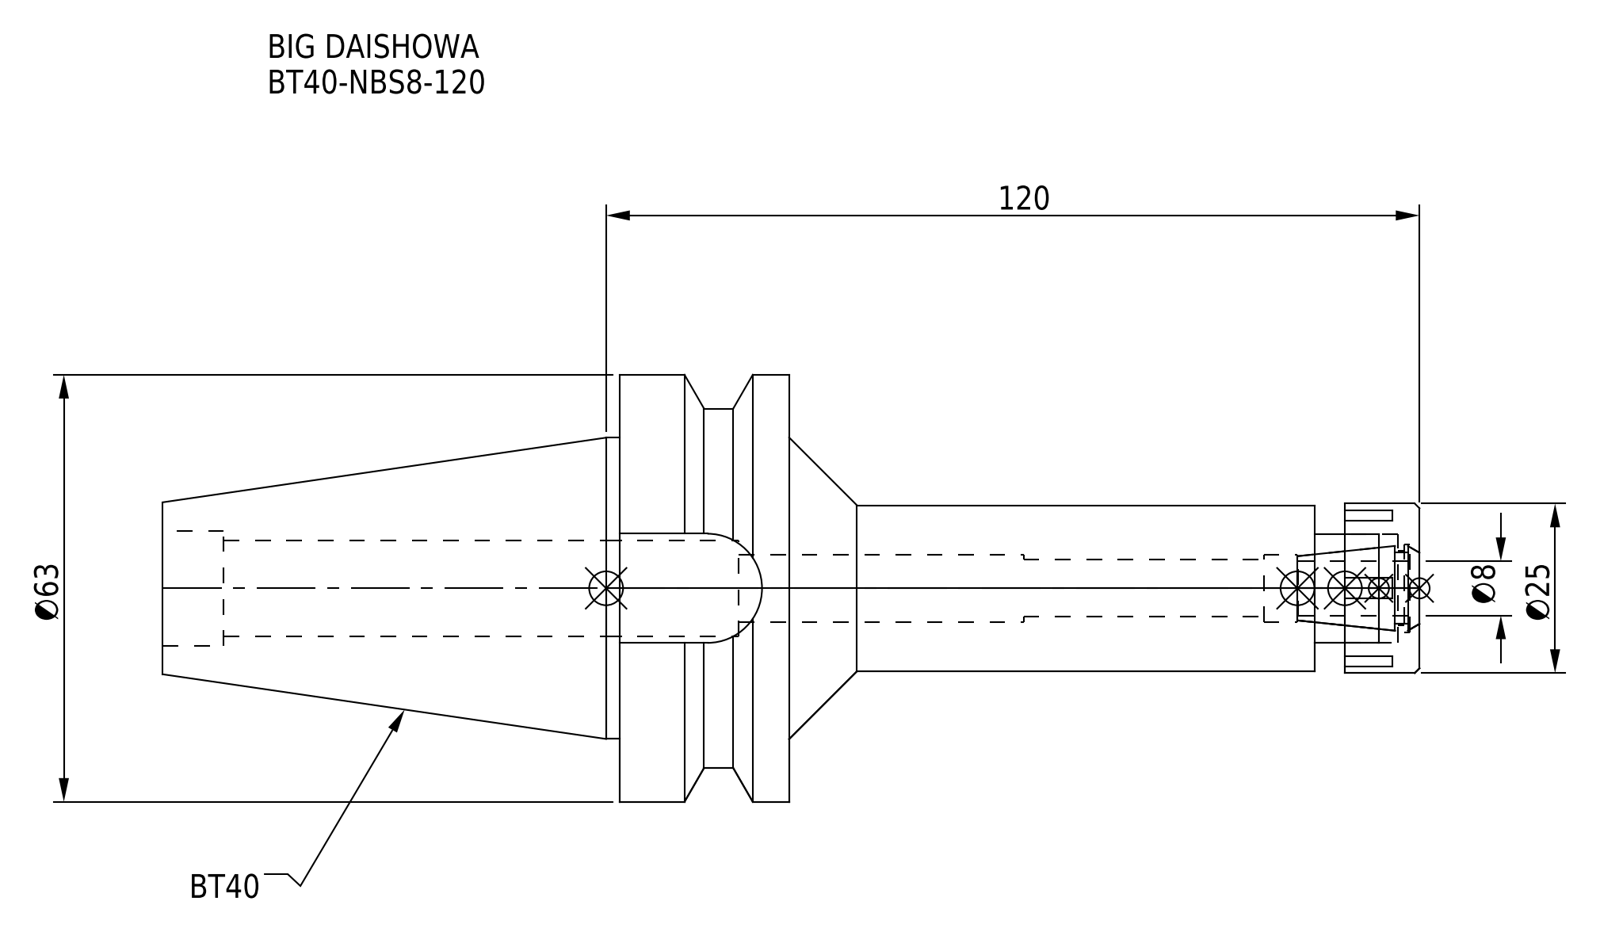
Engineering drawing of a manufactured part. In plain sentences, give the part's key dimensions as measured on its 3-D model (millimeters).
The part is named "BT40-NBS8-120-FreeParts; DXF_TEMP_ASSY_ASM_4_ASM.stp; NBN8_1.stp; BT40-NBS8-120_1.stp (+3 more)". Its 3-D file was written by "SolidWorks 2019 (CONFIG_CONTROL_DESIGN)". It is 2 solids with 93 faces: 45 planar, 34 cylindrical and 14 other. Overall it measures 185.4 by 63 by 63 millimeters. Its volume is 160 096 cubic millimeters and its surface area 33 717 square millimeters. Round holes: 1 of diameter 8.4, 1 of diameter 10, 1 of diameter 11, 1 of diameter 13, 1 of diameter 14.2, 1 of diameter 16, 1 of diameter 17. Round bosses or shafts: 1 of diameter 63, 1 of diameter 53, 1 of diameter 44.45, 1 of diameter 25, 1 of diameter 24.5. Partial cylindrical surfaces (rounded edges, fillets, slot ends): 1 of radius 8.05. The main face-to-face distances are 25, 118, 93, 45, 185.4, 92.4, 67.4, 15.5, 77.5, 102.5.
